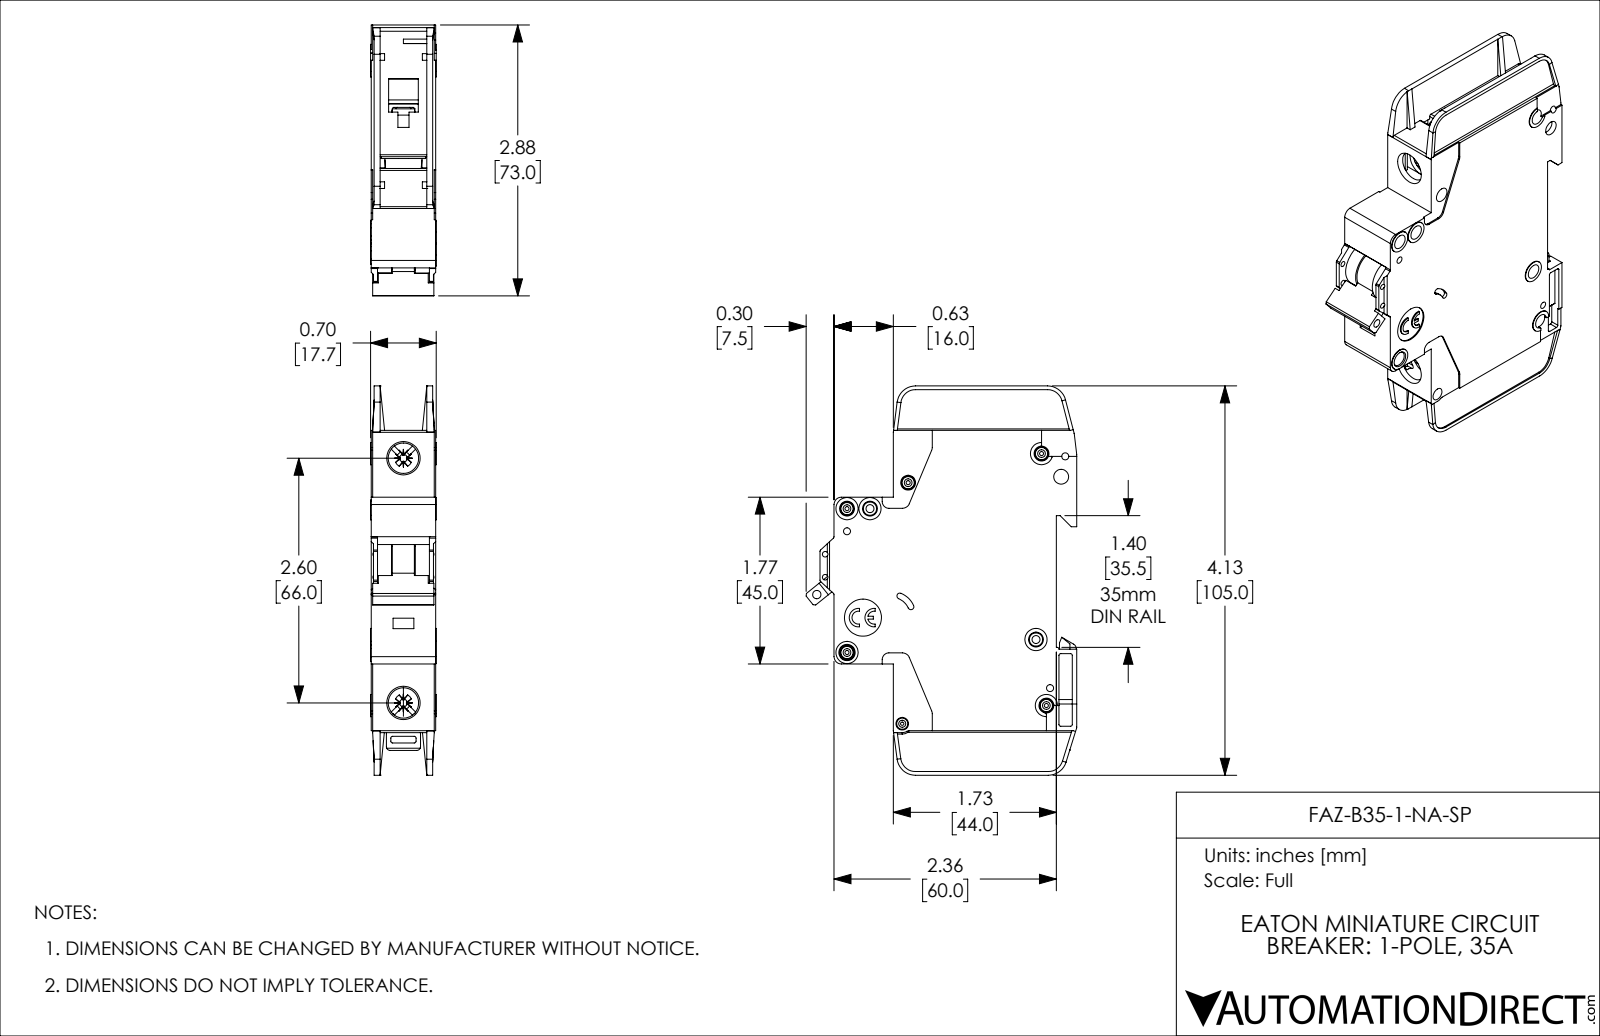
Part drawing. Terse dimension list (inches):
name: FAZ-B35-1-NA-SP
written by: SolidWorks 2019 (AUTOMOTIVE_DESIGN)
unit: in
bodies: 1 solid, 1127 faces (671 planar, 357 cylindrical, 99 other)
size: 4.134 × 2.876 × 0.697
volume: 4.682 in³; area: 41.01 in²
holes: 8× ⌀0.157, 5× ⌀0.043, 4× ⌀0.075, 2× ⌀0.059, 2× ⌀0.085, 2× ⌀0.323, 1× ⌀0.035, 1× ⌀0.089, 1× ⌀0.098, 1× ⌀0.134, 1× ⌀0.394
bosses: 5× ⌀0.13, 4× ⌀0.236, 2× ⌀0.118, 1× ⌀0.098
rounds: 42× R0.02, 10× R0.016, 10× R0.039, 8× R0.079, 5× R0.197, 4× R0.008, 4× R0.026, 4× R0.043
face distances: 0.047, 0.685, 0.591, 0.638, 0.094, 0.543, 0.016, 0.031, 0.496, 0.575
hole spacings: 0.244, 0.537, 0.87, 0.189, 0.199, 0.204, 0.221, 0.24
